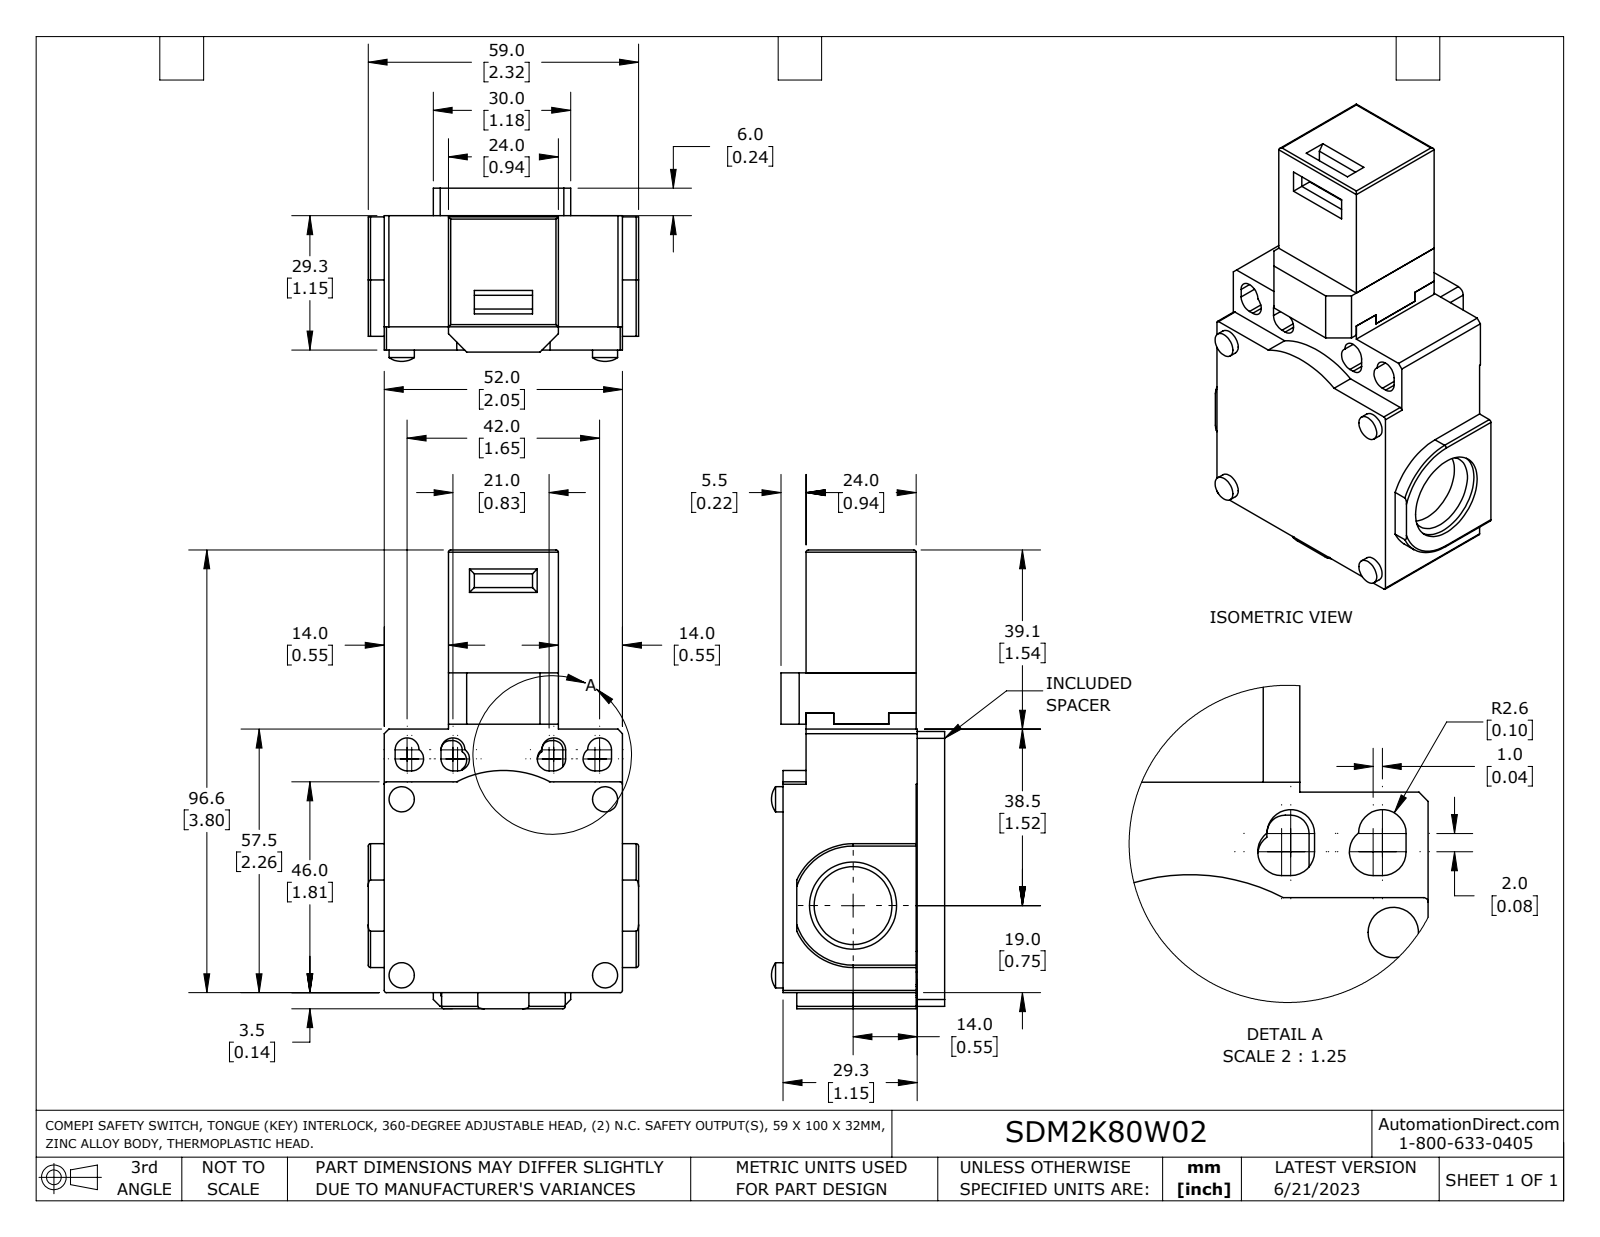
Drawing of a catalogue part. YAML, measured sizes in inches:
part_name: "SDM2K80W02"
step_written_by: "SolidWorks 2021 (AUTOMOTIVE_DESIGN)"
units: inches
bodies: {solids: 4, faces: 287, planar: 166, cylindrical: 105, other: 16}
overall_size: [3.941, 2.323, 1.488]
volume: 6.697
surface_area: 45.4
round_holes:
  - {diameter: 0.669, count: 2}
  - {diameter: 0.748, count: 2}
  - {diameter: 0.591, count: 1}
round_bosses_or_shafts:
  - {diameter: 0.217, count: 4}
partial_cylinders:
  - {radius: 0.016, count: 24}
  - {radius: 0.079, count: 24}
  - {radius: 0.02, count: 14}
  - {radius: 0.102, count: 12}
  - {radius: 0.059, count: 2}
  - {radius: 0.091, count: 2}
  - {radius: 0.531, count: 2}
  - {radius: 0.394, count: 1}
face_to_face_distances: [0.551, 1.144, 1.496, 0.945, 0.236, 1.154, 0.138, 0.199, 0.955, 2.047]
hole_center_spacings: [0.069]
